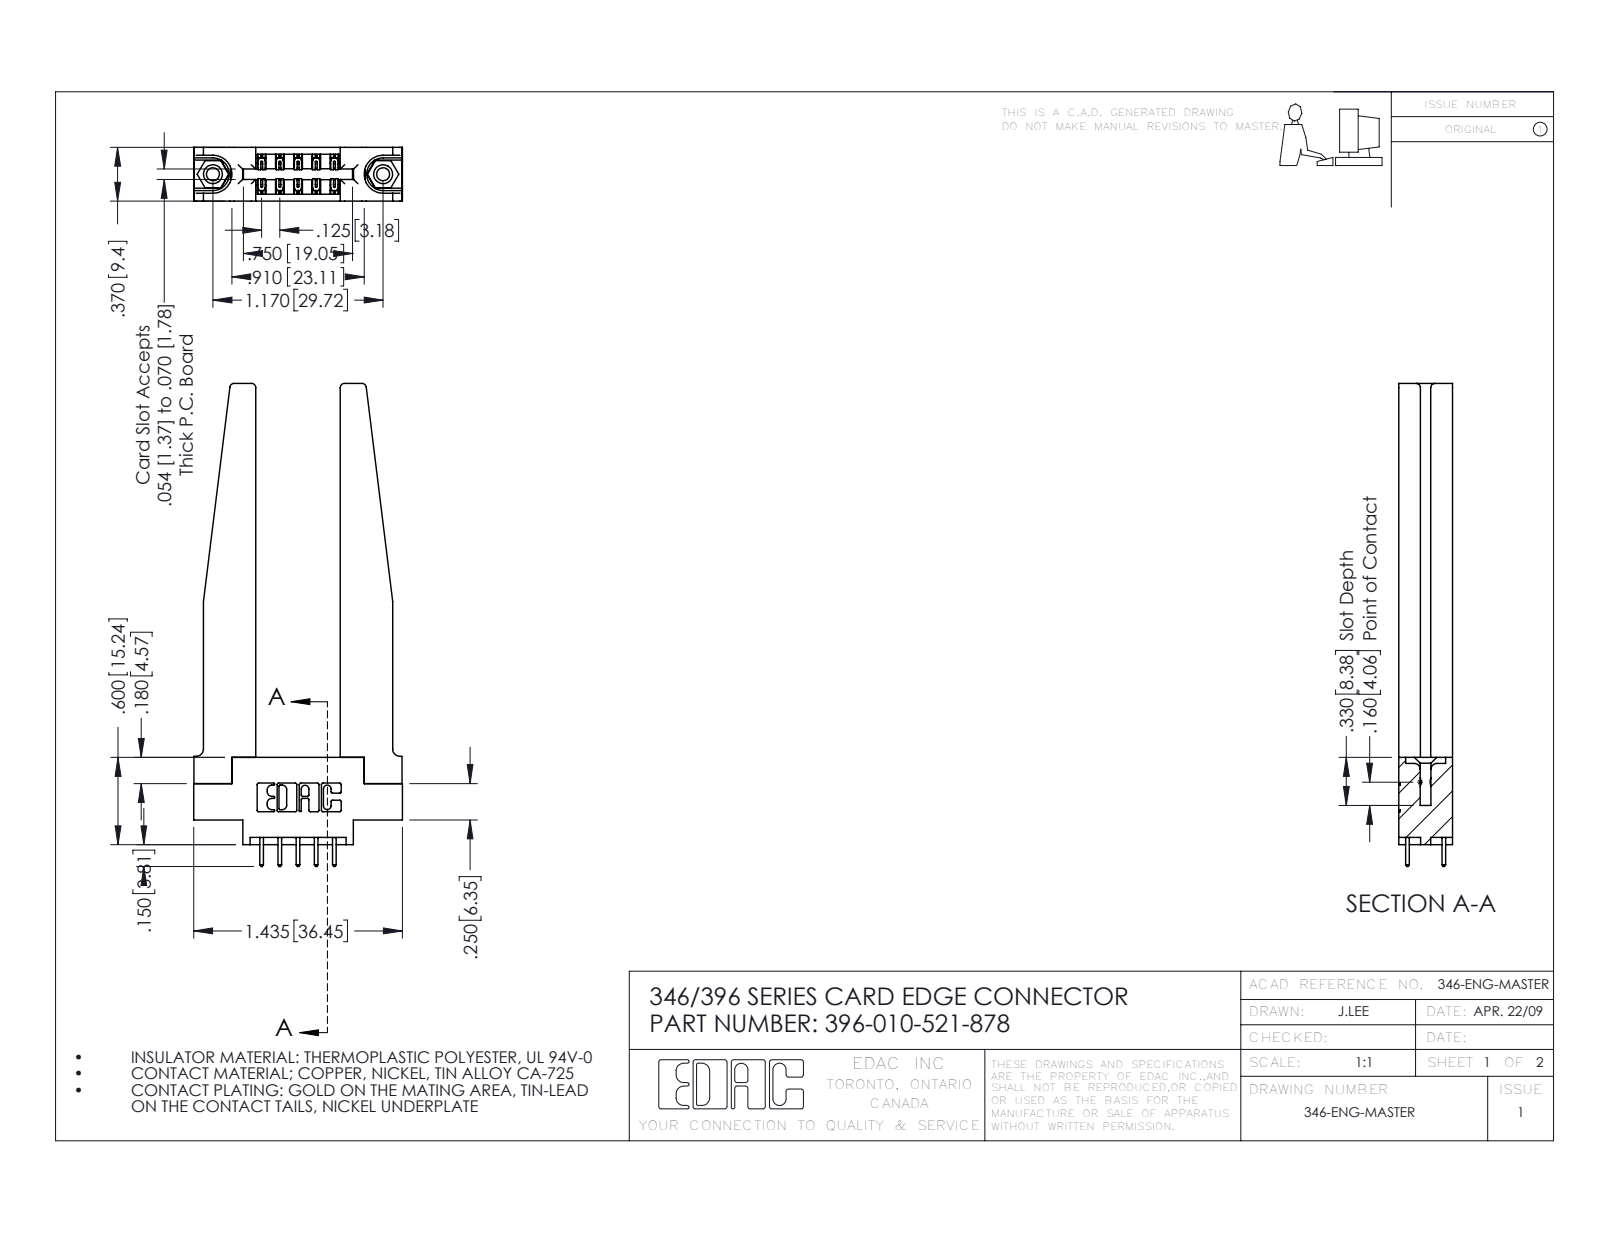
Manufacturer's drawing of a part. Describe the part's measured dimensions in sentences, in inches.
The part is named "346 Part_0.170 Offset - 0.156 Dia-TH; 345-250-001_345-250-001-102; 346-220-078_345-220-078; 345-292-001_345-293-121 (+1 more)". Its 3-D file was written by "SolidWorks 2016 (CONFIG_CONTROL_DESIGN)". It is 15 solids with 880 faces: 572 planar, 256 cylindrical and 52 other. Overall it measures 3.32 by 1.435 by 0.37 inches. Its volume is 0.611 cubic inches and its surface area 16.09 square inches. Round holes: 2 of diameter 0.089, 2 of diameter 0.125, 2 of diameter 0.156, 1 of diameter 0.064. Round bosses or shafts: 2 of diameter 0.155. Partial cylindrical surfaces (rounded edges, fillets, slot ends): 22 of radius 0.01, 15 of radius 0.006, 10 of radius 0.01, 8 of radius 0.03, 6 of radius 0.007, 6 of radius 0.031, 3 of radius 0.026, 2 of radius 0.014. The main face-to-face distances are 0.37, 0.15, 0.22, 0.25, 0.581, 0.148, 0.072, 0.102, 0.048, 0.322. The hole center spacings are 0.246, 0.969, 1.17.
